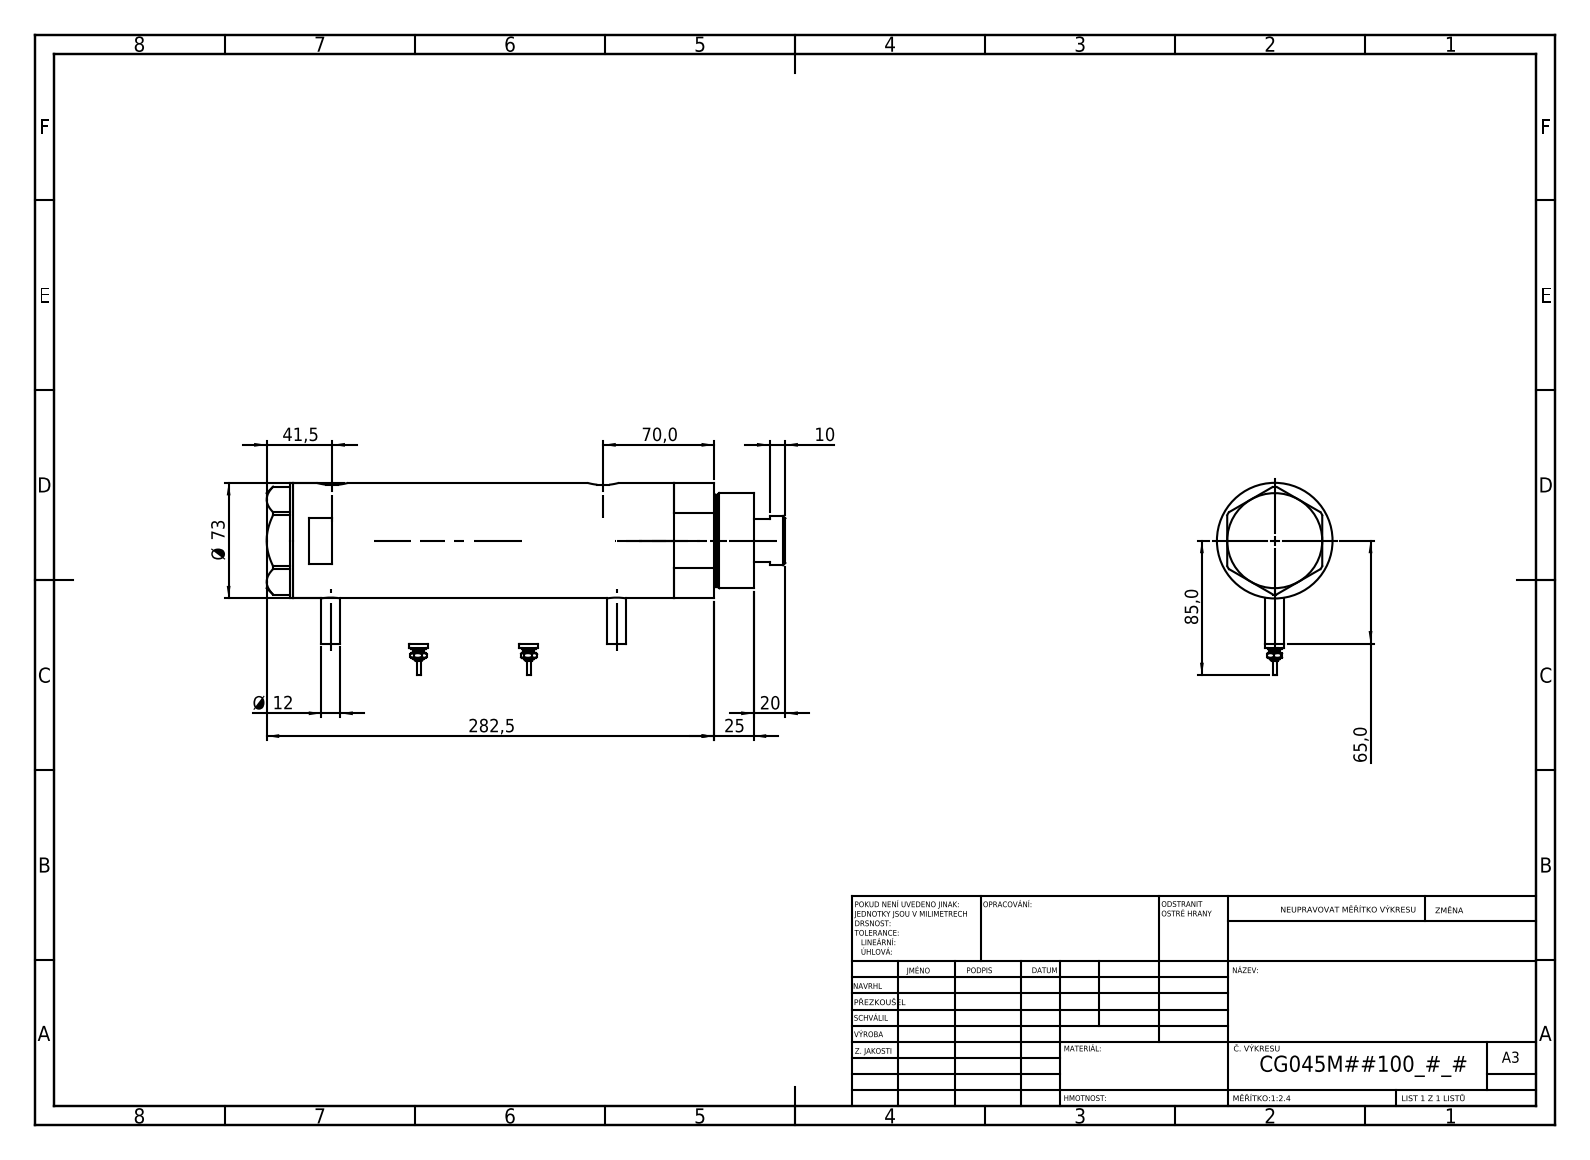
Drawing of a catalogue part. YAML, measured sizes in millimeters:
part_name: "V270CG_MIDDLE; V270CG_FRONT; V270CG_BACK; Switch (+1 more)"
step_written_by: "SolidWorks 2019 (CONFIG_CONTROL_DESIGN)"
units: millimeters
bodies: {solids: 6, faces: 212, planar: 77, cylindrical: 71, other: 64}
overall_size: [327.5, 121.5, 73]
volume: 1167000
surface_area: 188093
round_holes:
  - {diameter: 12.5, count: 2}
  - {diameter: 13.16, count: 2}
  - {diameter: 10.5, count: 1}
  - {diameter: 32, count: 1}
  - {diameter: 33.5, count: 1}
  - {diameter: 45, count: 1}
  - {diameter: 48, count: 1}
  - {diameter: 64, count: 1}
round_bosses_or_shafts:
  - {diameter: 12, count: 4}
  - {diameter: 9, count: 2}
  - {diameter: 7, count: 2}
  - {diameter: 4.5, count: 2}
  - {diameter: 2.5, count: 2}
  - {diameter: 73, count: 1}
  - {diameter: 60, count: 1}
  - {diameter: 58, count: 1}
partial_cylinders:
  - {radius: 10, count: 2}
face_to_face_distances: [170, 196, 26, 16.5, 42.5, 212.5, 2, 291, 70, 307.5]
hole_center_spacings: [1, 8.5, 171, 172, 179.5, 180.5]
